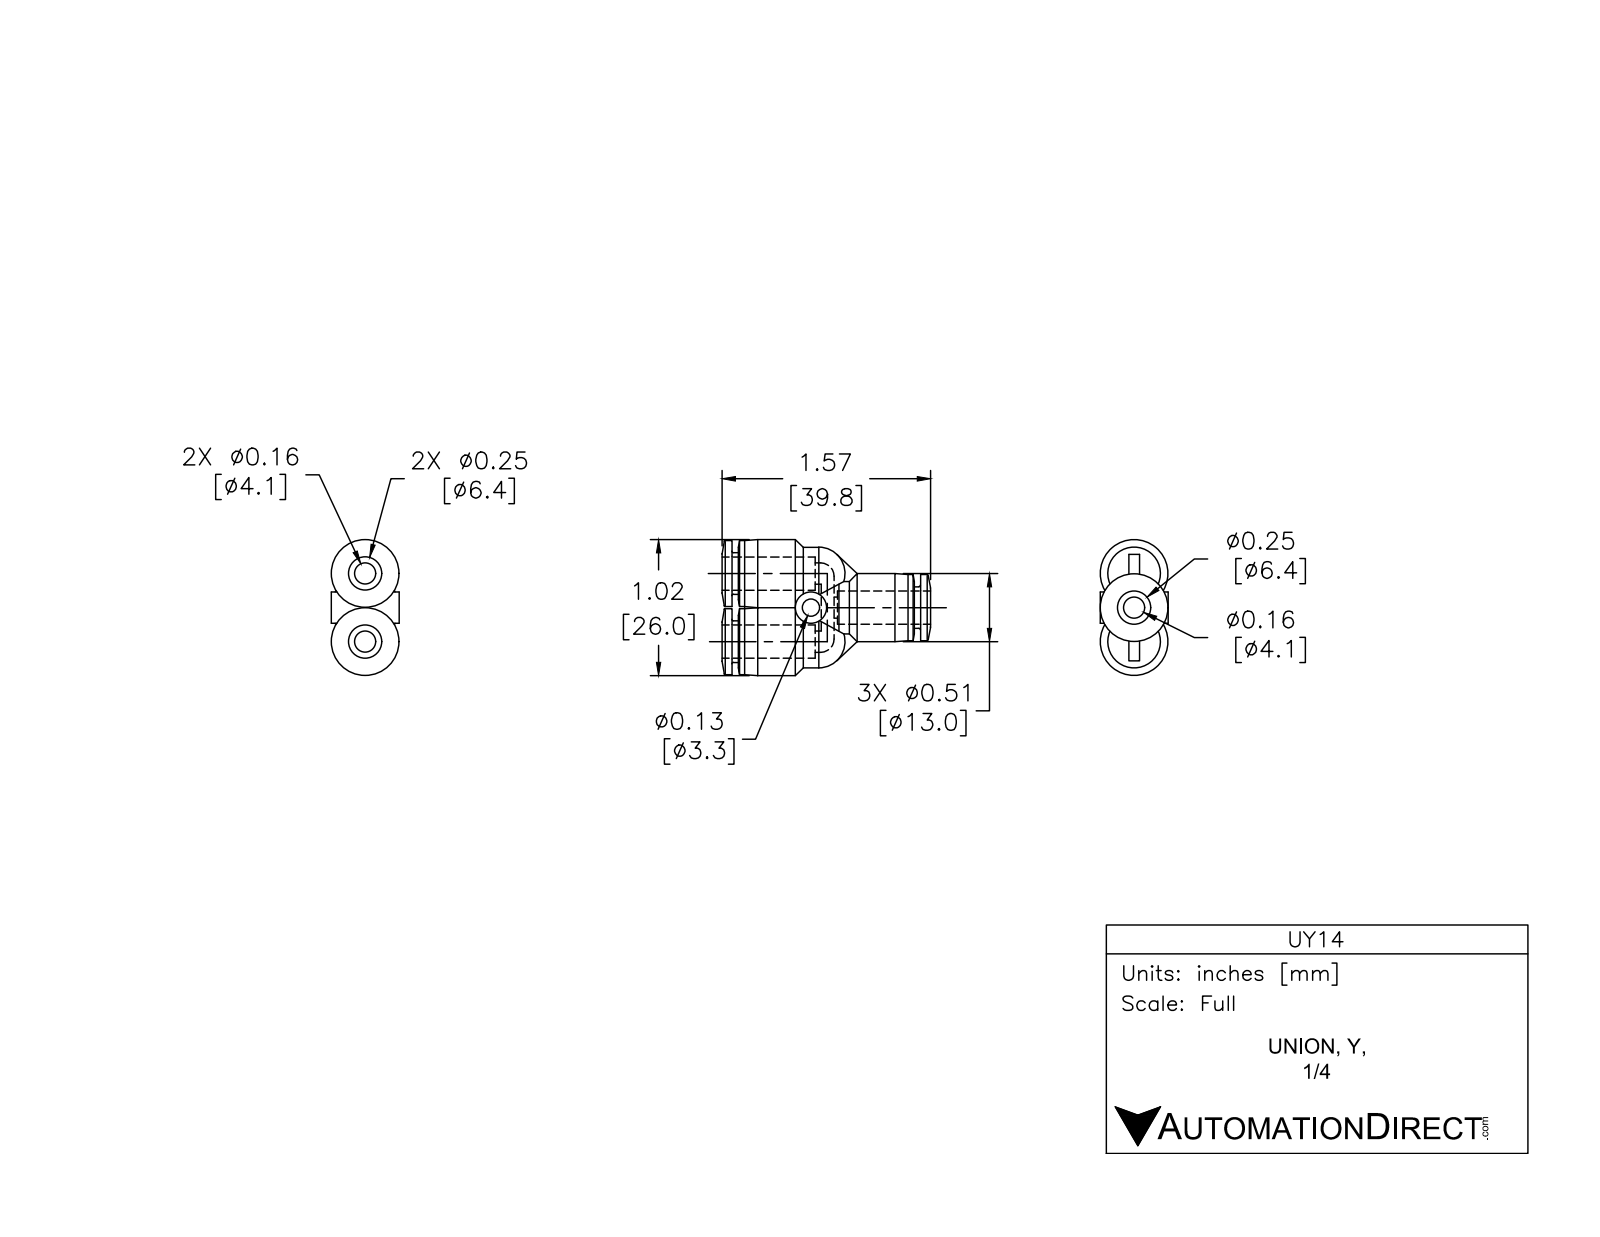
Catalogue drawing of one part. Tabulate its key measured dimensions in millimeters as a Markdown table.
| quantity | value |
| --- | --- |
| part name | UY14 |
| STEP written by | SolidWorks 2015 (AUTOMOTIVE_DESIGN) |
| units | millimeters |
| bodies | 1 solid, 119 faces (18 planar, 43 cylindrical, 58 other) |
| overall size | 39.8 × 26 × 13 |
| volume | 5 100 mm³ |
| surface area | 4 523 mm² |
| round holes (diameter × count) | 6.6 × 3, 3.3 × 1 |
| round bosses / shafts (diameter × count) | 13 × 3, 12.6 × 3, 8 × 3, 10 × 1, 6 × 1 |
| partial cylindrical surfaces (radius × count) | 5 × 2 |
| main face-to-face distances | 1.2, 34.8, 36, 16, 20, 14.8, 18.8, 33.6, 5.5, 7.5 |
| hole center spacings | 6.5, 13 |
